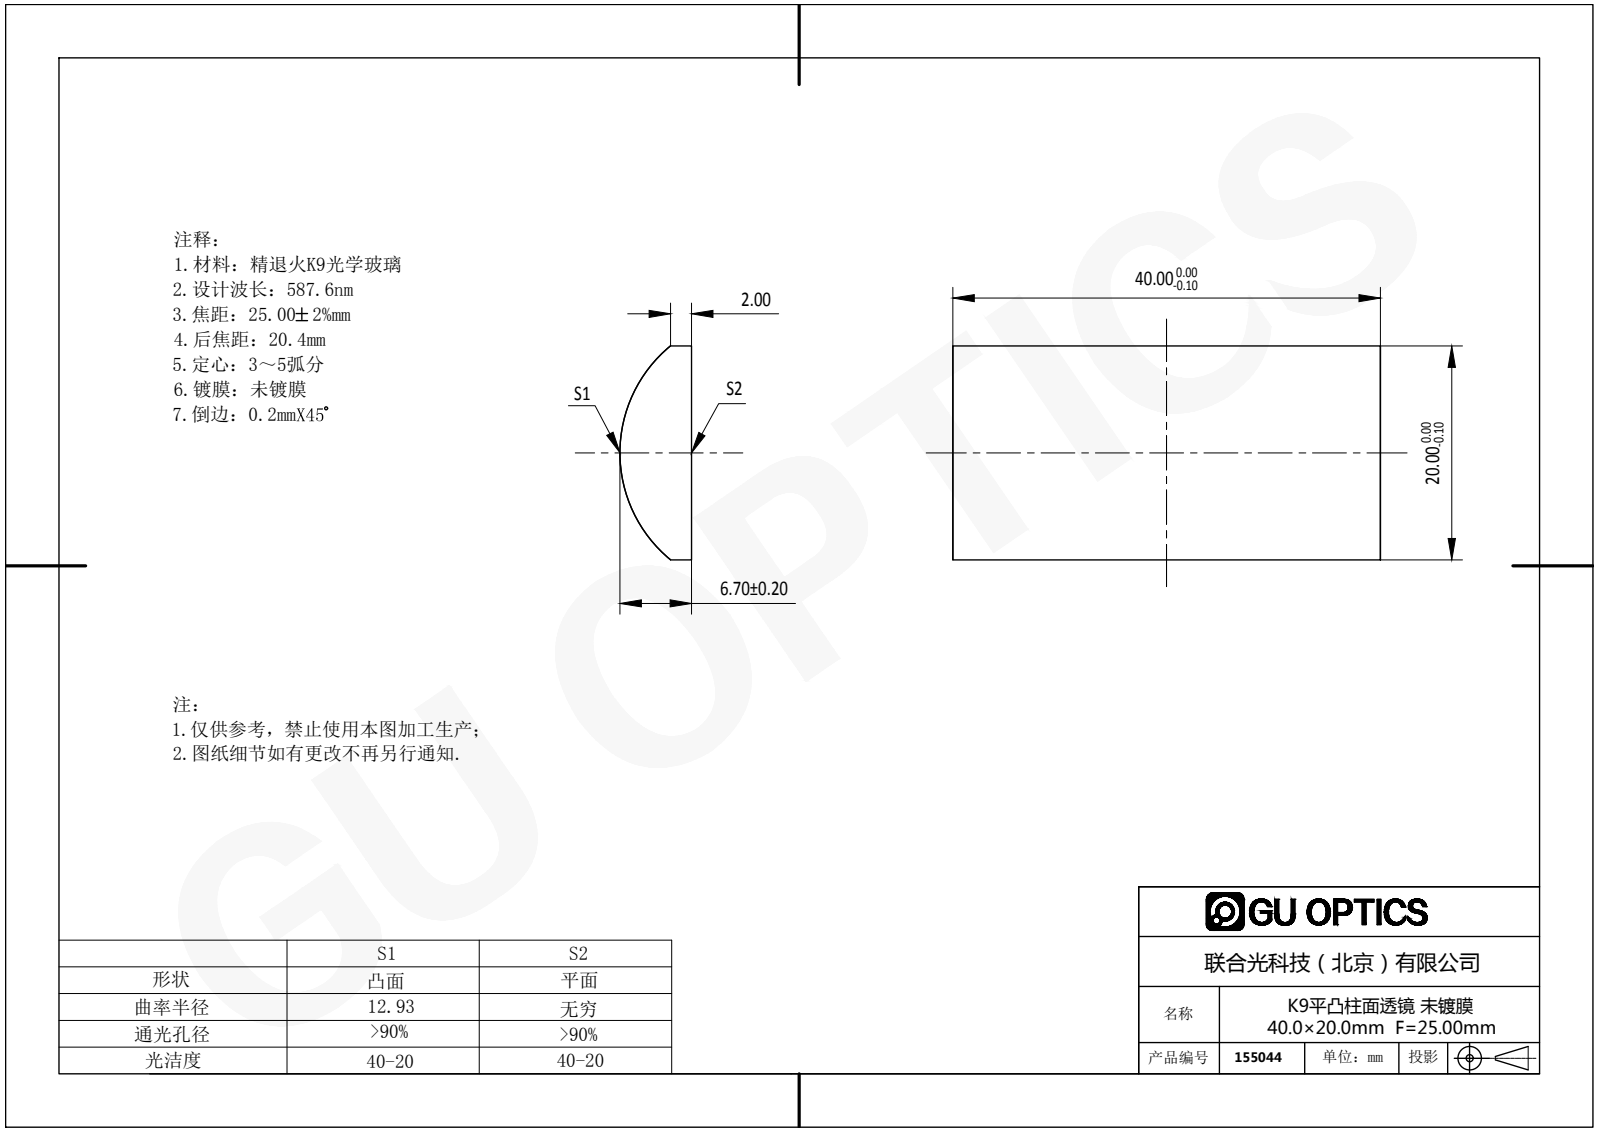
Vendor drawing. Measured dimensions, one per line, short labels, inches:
name: 155044
written by: SolidWorks 2016 (AUTOMOTIVE_DESIGN)
unit: in
bodies: 1 solid, 6 faces (5 planar, 1 cylindrical, 0 other)
size: 1.575 × 0.787 × 0.264
volume: 0.257 in³; area: 3.227 in²
rounds: 1× R0.509
face distances: 1.575, 0.787
